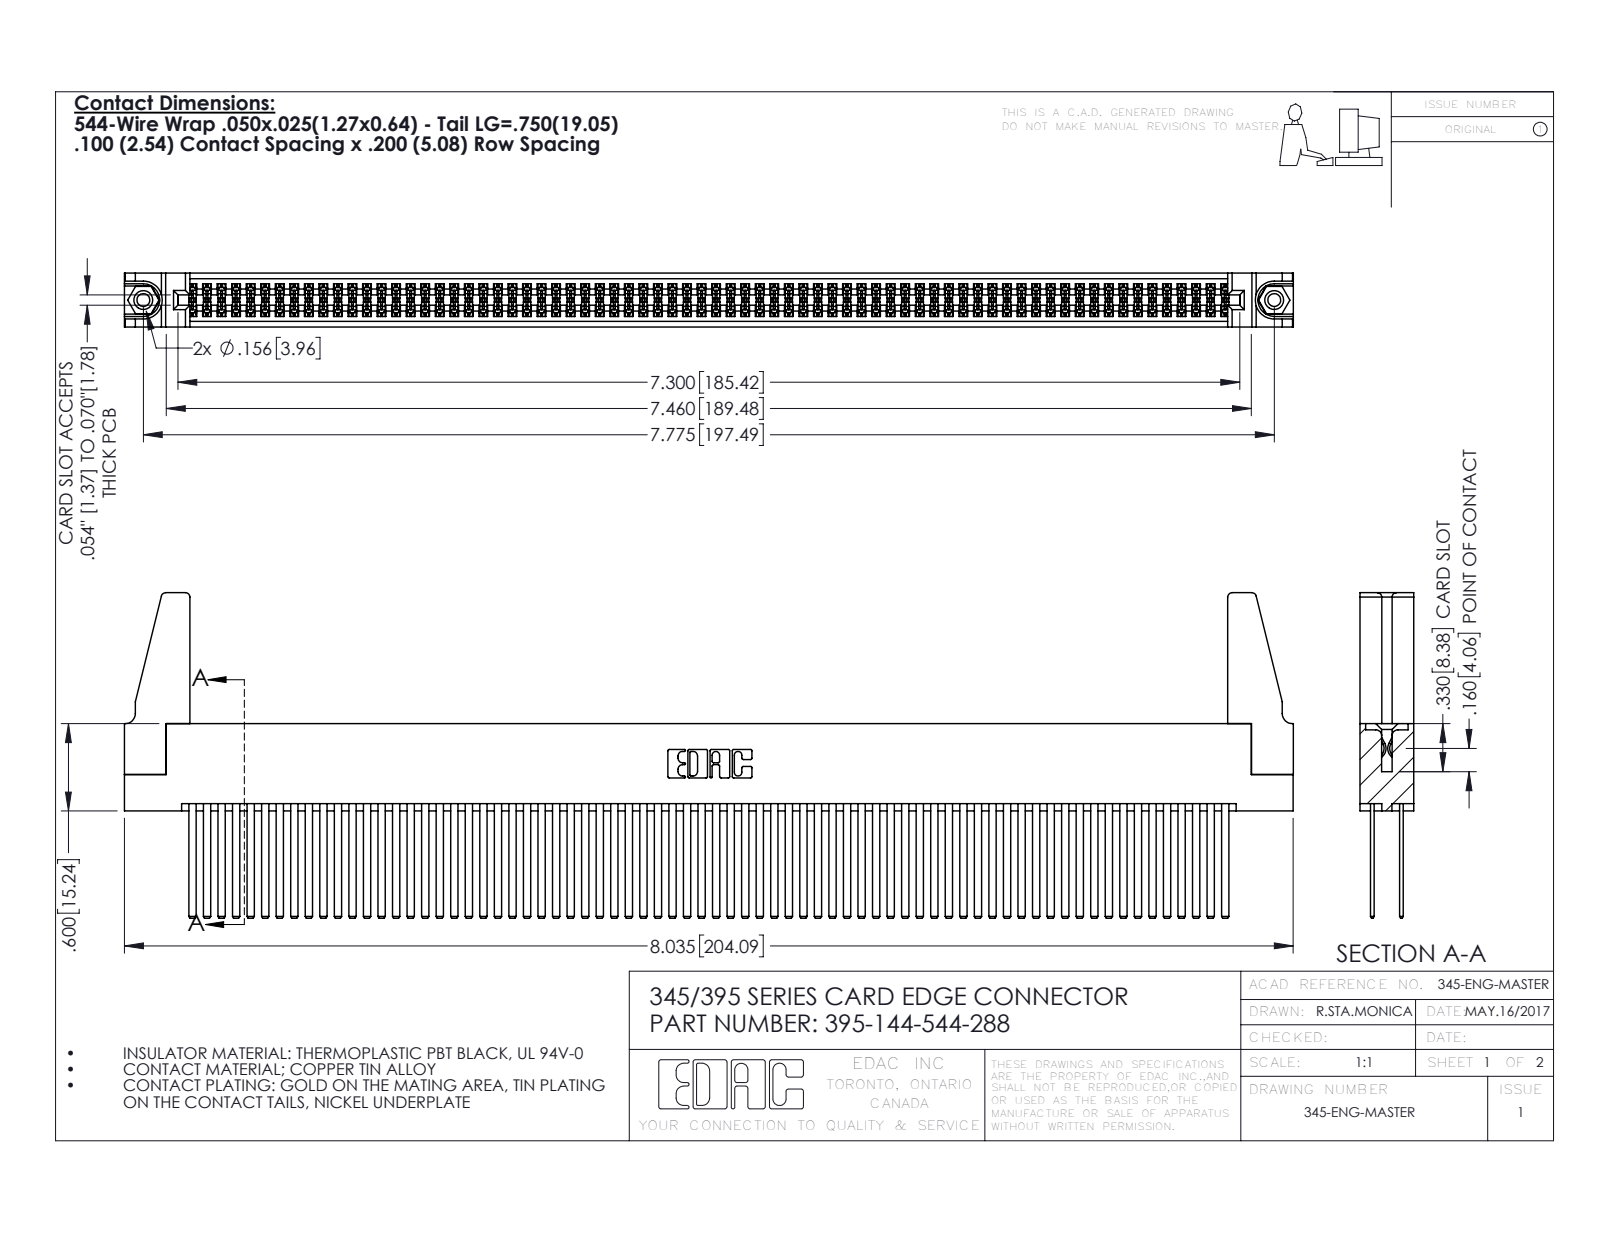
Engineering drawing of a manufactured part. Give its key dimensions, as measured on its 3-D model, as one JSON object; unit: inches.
{"part_name": "345 Part_Flush Mounting Lugs - 0.156 Dia-TH; 345-220-078_345-220-088; 345-292-001_345-293-144; 345-250-001_345-250-001-102 (+1 more)", "step_written_by": "SolidWorks 2016 (CONFIG_CONTROL_DESIGN)", "units": "inches", "bodies": {"solids": 149, "faces": 6586, "planar": 4328, "cylindrical": 2242, "other": 16}, "overall_size": [8.036, 2.237, 0.37], "volume_in3": 1.549, "surface_area_in2": 65.6, "round_holes": [[0.089, 2], [0.125, 2], [0.156, 2], [0.064, 1]], "round_bosses_or_shafts": [[0.155, 2]], "partial_cylinders_radius": [[0.006, 216], [0.01, 22], [0.03, 8], [0.007, 6], [0.031, 6], [0.026, 3], [0.014, 2], [0.019, 2]], "face_to_face_distances": [0.072, 0.298, 0.2, 0.098, 0.272, 0.025, 0.225, 0.37, 0.175, 0.149], "hole_center_spacings": [0.27, 7.539, 7.775]}
